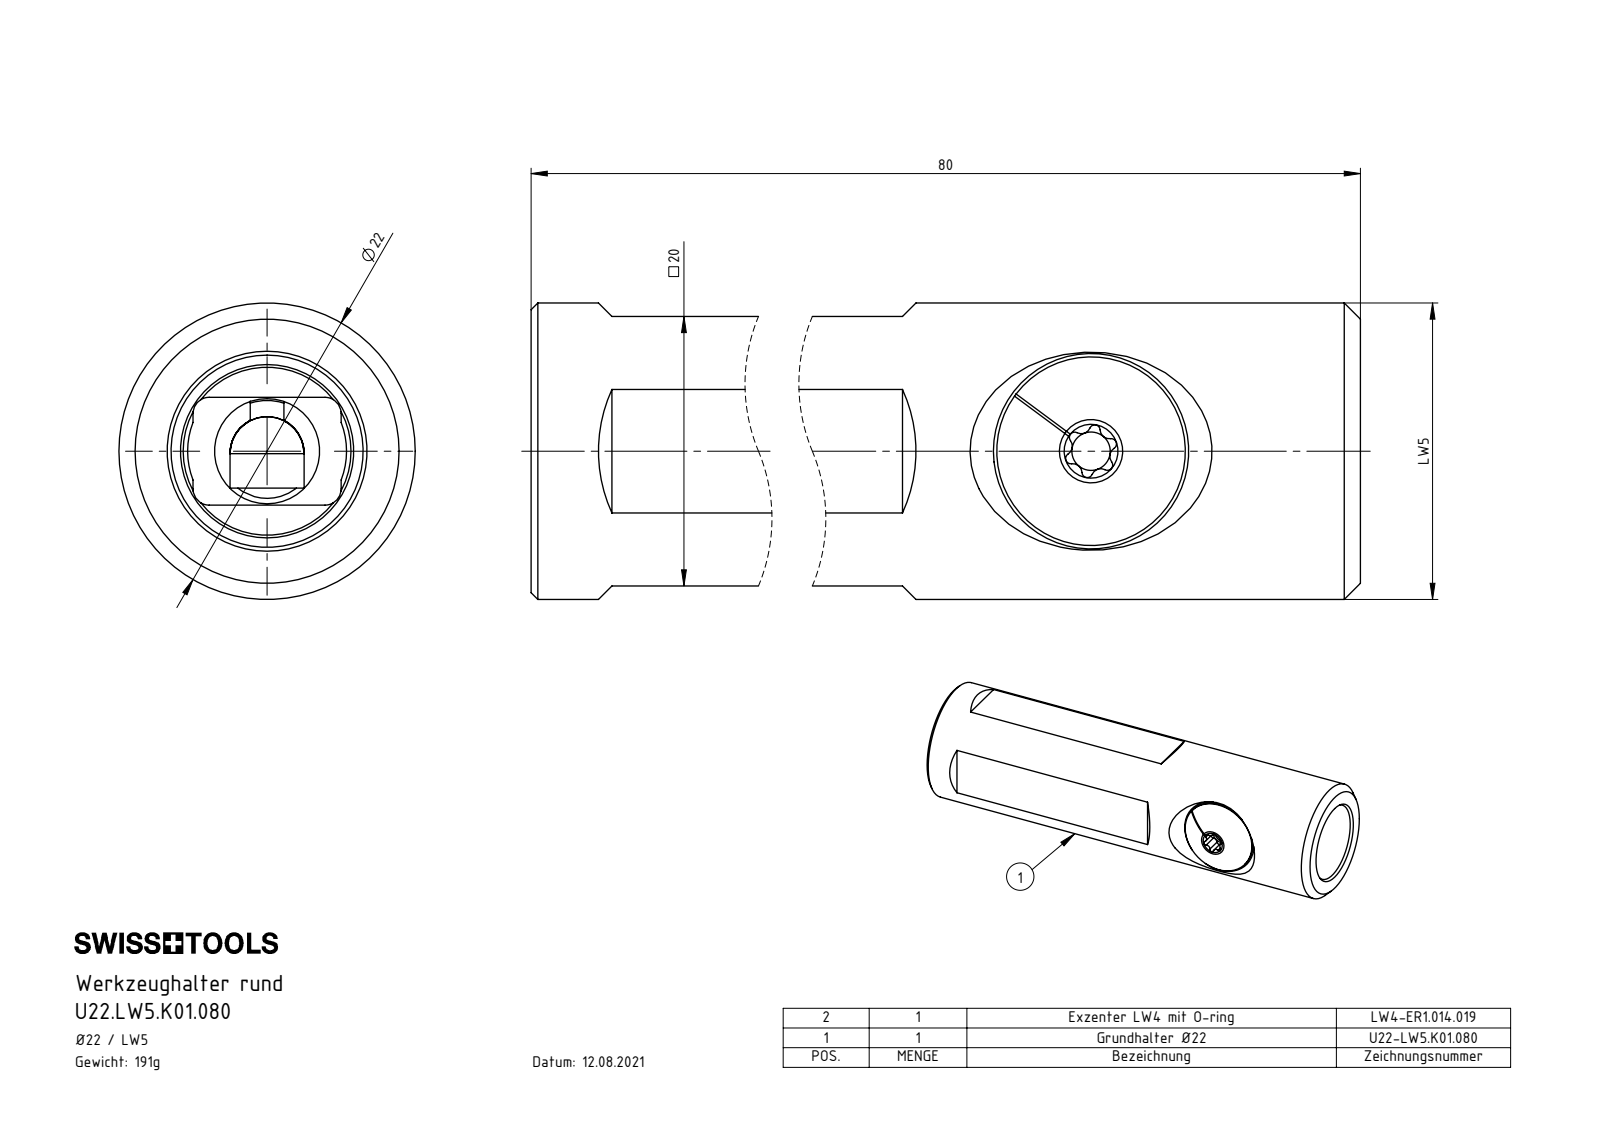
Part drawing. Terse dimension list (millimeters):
name: LW4-ER1.014.019_A_Standard<Wie bearbeitet>; U22-LW5.K01.080_A; U22.LW5.K01.080; DIN 3771 - 10x1 (+1 more)
written by: SolidWorks 2017 (AUTOMOTIVE_DESIGN)
unit: mm
bodies: 4 solids, 132 faces (54 planar, 43 cylindrical, 35 other)
size: 80 × 22 × 22
volume: 24 321 mm³; area: 9 643 mm²
holes: 1× ⌀1, 1× ⌀2.85, 1× ⌀7, 1× ⌀7.8, 1× ⌀12.86
bosses: 1× ⌀22, 1× ⌀14, 1× ⌀12, 1× ⌀10.2
rounds: 6× R0.4, 6× R0.69, 4× R1.2, 2× R2.75, 2× R4.15, 1× R4.1, 1× R4.7, 1× R5.9
face distances: 20, 2.1, 80, 17.9, 2, 16, 1.1, 12.6, 4, 6
